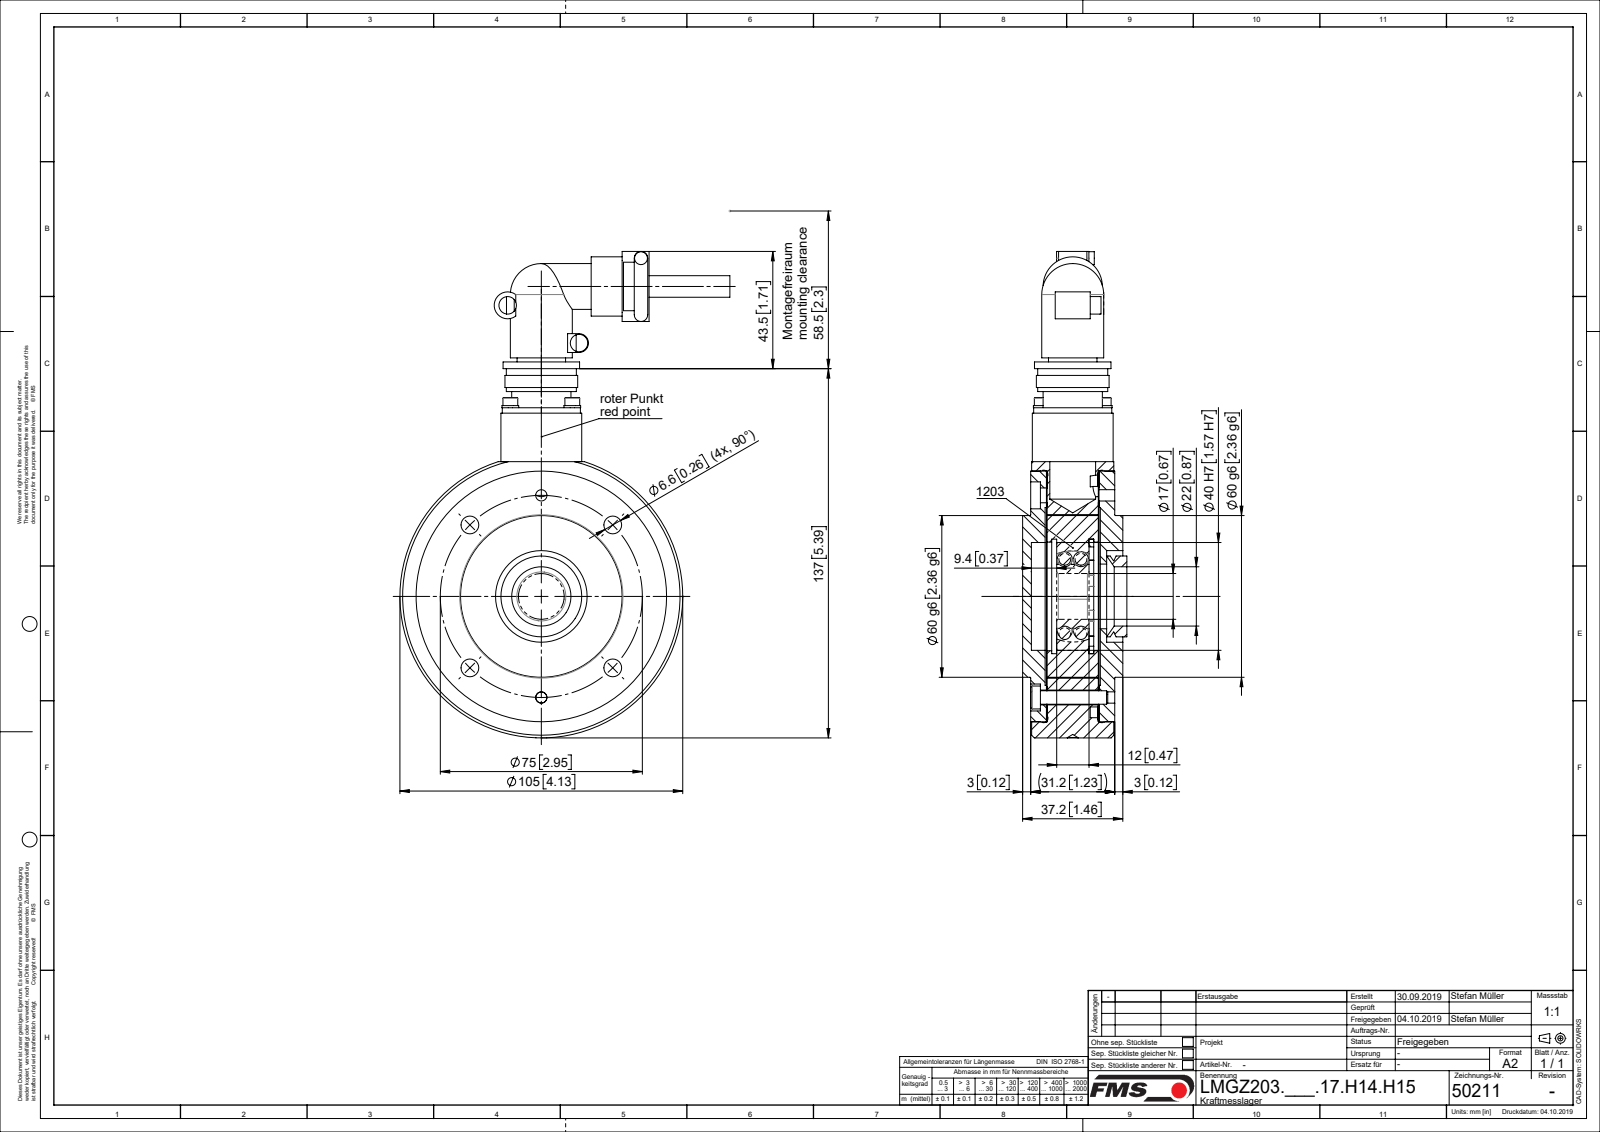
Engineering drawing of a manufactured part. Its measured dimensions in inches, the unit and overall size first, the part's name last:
Units: inches
Overall size (bounding box): 7.106 × 4.823 × 1.465
Round holes (diameter × count): ⌀0.102 ×4, ⌀0.126 ×4, ⌀0.134 ×4, ⌀0.138 ×4, ⌀0.26 ×4, ⌀0.157 ×2, ⌀0.209 ×2, ⌀0.217 ×2, ⌀0.394 ×2, ⌀0.669 ×1, ⌀0.866 ×1, ⌀0.906 ×1
Round bosses / shafts (diameter × count): ⌀0.244 ×4, ⌀0.217 ×4, ⌀0.118 ×4, ⌀0.866 ×2, ⌀0.315 ×2, ⌀0.256 ×2, ⌀0.189 ×2, ⌀4.134 ×1
Partial cylindrical surfaces — rounded edges, fillets, slot ends (radius × count): R0.098 ×2, R0.138 ×1, R0.197 ×1
Main face-to-face distances: 0.758, 0.748, 0.23, 0.988, 0.24, 0.998, 0.768, 0.787, 0.118, 0.02
Hole centre spacings: 1.476, 0.64, 0.906, 1.13, 2.088, 2.728, 1.281, 2.953
Volume: 18.07 in³ · Surface area: 162.3 in²
Bodies: 19 solids, 365 faces (113 planar, 215 cylindrical, 37 other)
Part name (STEP PRODUCT): L50211; L4936404; TEIL1; L47958 (+8 more)
STEP written by: Mechanical Desktop 2007 (CONFIG_CONTROL_DESIGN)
